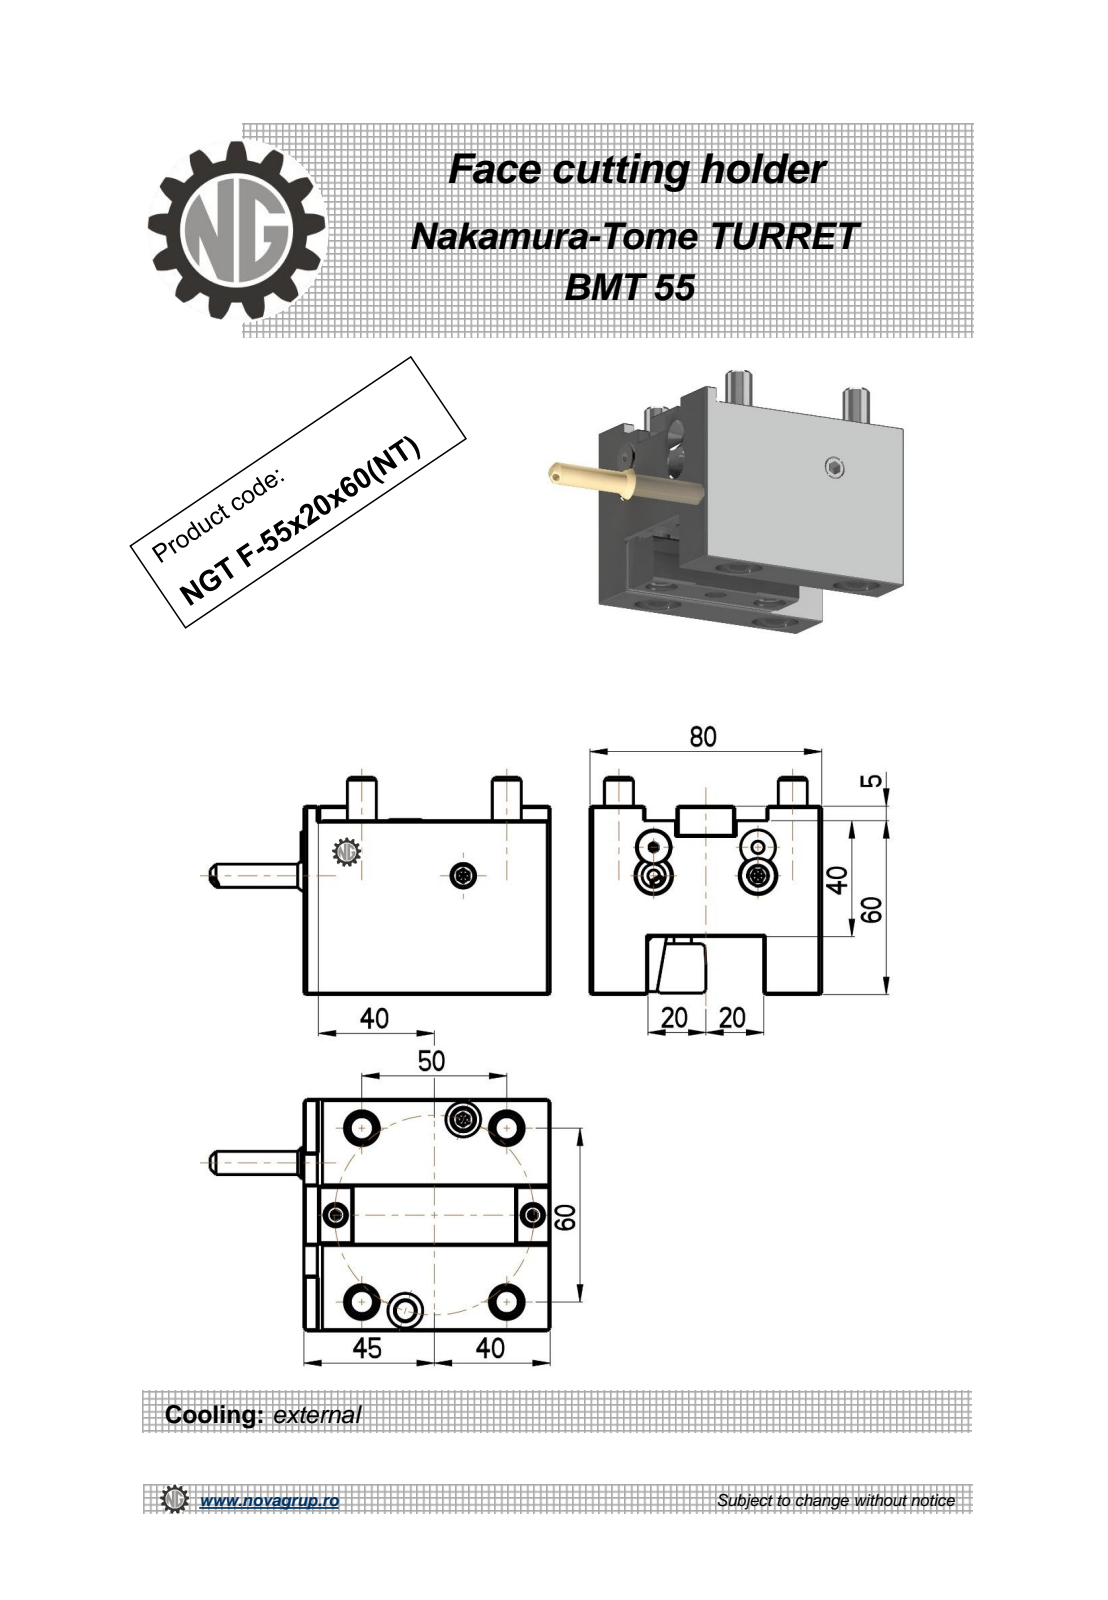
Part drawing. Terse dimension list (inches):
name: NGT_F_55_20_60_NT
written by: PRO/ENGINEER BY PARAMETRIC TECHNOLOGY CORPORATION, 2010280 (CONFIG_CONTROL_DESIGN)
unit: in
bodies: 1 solid, 199 faces (123 planar, 43 cylindrical, 33 other)
size: 4.62 × 3.15 × 2.953
volume: 22.17 in³; area: 67.3 in²
holes: 2× ⌀0.472, 1× ⌀0.118, 1× ⌀0.197, 1× ⌀0.268
bosses: 4× ⌀0.394, 3× ⌀0.236, 1× ⌀0.441, 1× ⌀0.315
rounds: 6× R0.009, 6× R0.016, 1× R0.039
face distances: 0.787, 2.362, 3.15, 1.575, 3.346, 0.394, 0.197, 1.181, 2.165, 1.378
hole spacings: 2.715
